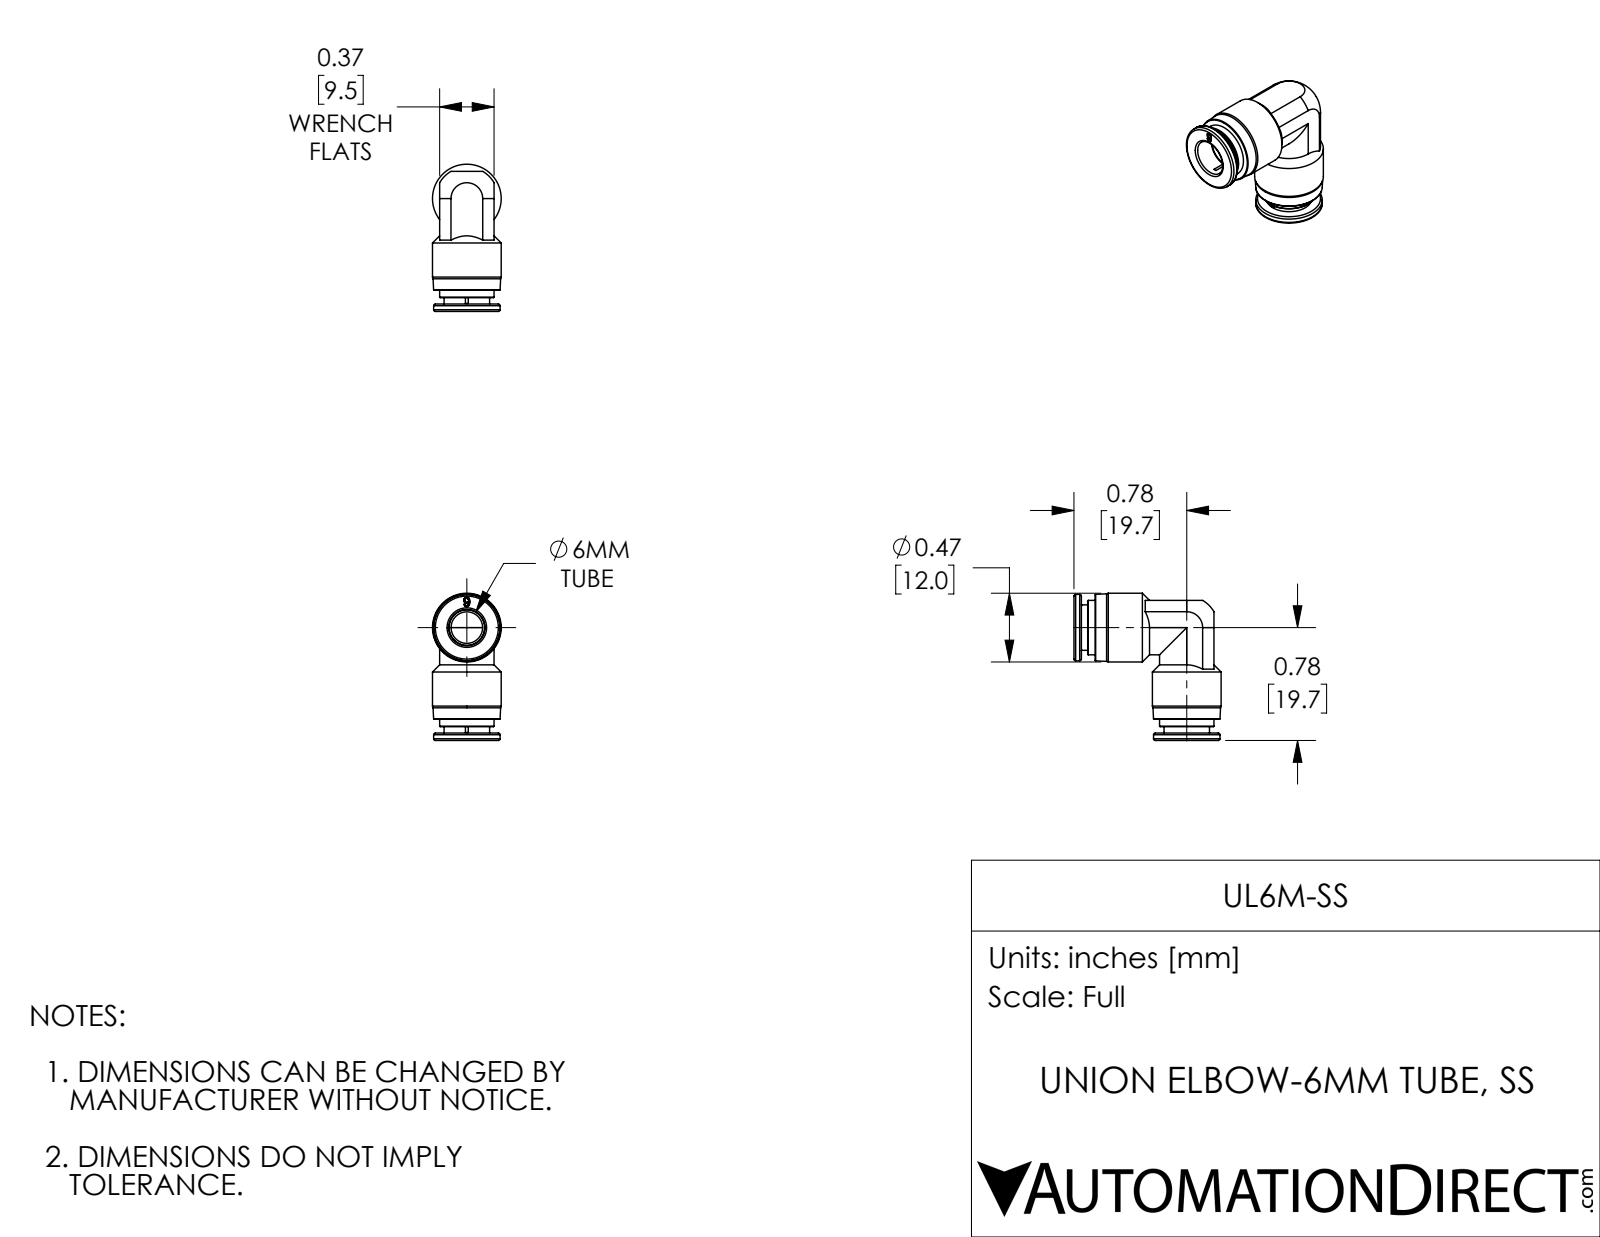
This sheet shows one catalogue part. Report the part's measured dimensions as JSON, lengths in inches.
{"part_name": "UL6M-SS", "step_written_by": "SolidWorks 2017 (AUTOMOTIVE_DESIGN)", "units": "inches", "bodies": {"solids": 1, "faces": 148, "planar": 34, "cylindrical": 39, "other": 75}, "overall_size": [1.012, 1.012, 0.472], "volume_in3": 0.153, "surface_area_in2": 4.045, "round_holes": [[0.217, 2], [0.244, 2], [0.248, 2], [0.319, 2]], "round_bosses_or_shafts": [[0.472, 2], [0.457, 2], [0.374, 2], [0.313, 2]], "partial_cylinders_radius": [[0.217, 2]], "face_to_face_distances": [0.051, 0.963, 0.911, 0.094, 0.146, 0.817, 0.374, 0.043, 0.868, 0.177]}
